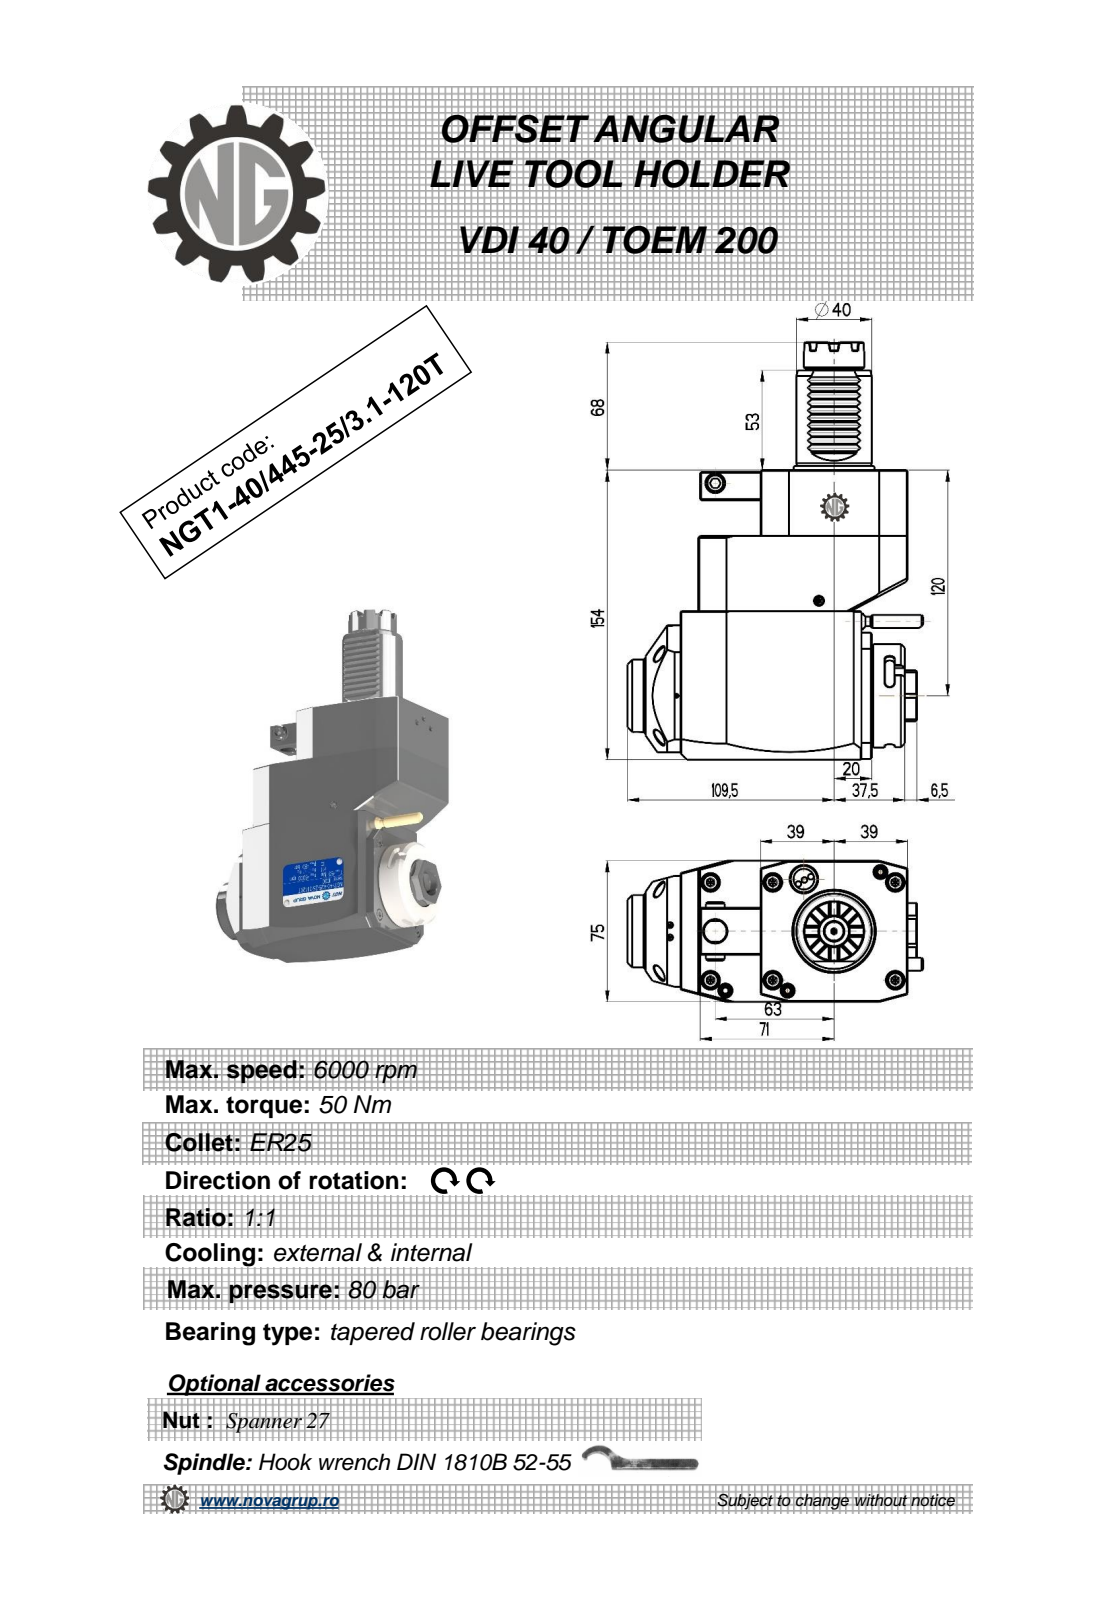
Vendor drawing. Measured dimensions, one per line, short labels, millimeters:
name: NGT1_40_445_25_3_1_120T
written by: PRO/ENGINEER BY PARAMETRIC TECHNOLOGY CORPORATION, 2010280 (CONFIG_CONTROL_DESIGN)
unit: mm
bodies: 1 solid, 415 faces (225 planar, 80 cylindrical, 110 other)
size: 222 × 156.83 × 75
volume: 1 277 000 mm³; area: 90 438 mm²
holes: 1× ⌀2.5, 1× ⌀3, 1× ⌀8.5, 1× ⌀9.5, 1× ⌀12, 1× ⌀18
bosses: 2× ⌀8.96, 1× ⌀55, 1× ⌀48, 1× ⌀40, 1× ⌀38.5, 1× ⌀32, 1× ⌀16.8, 1× ⌀10
rounds: 10× R0.3, 6× R2.5, 2× R180, 1× R0.5, 1× R8.6, 1× R15, 1× R24.5, 1× R37.5
face distances: 75, 154, 119, 19, 59, 111, 35, 92, 17.5, 33
hole spacings: 43.2, 75.07, 112.5
